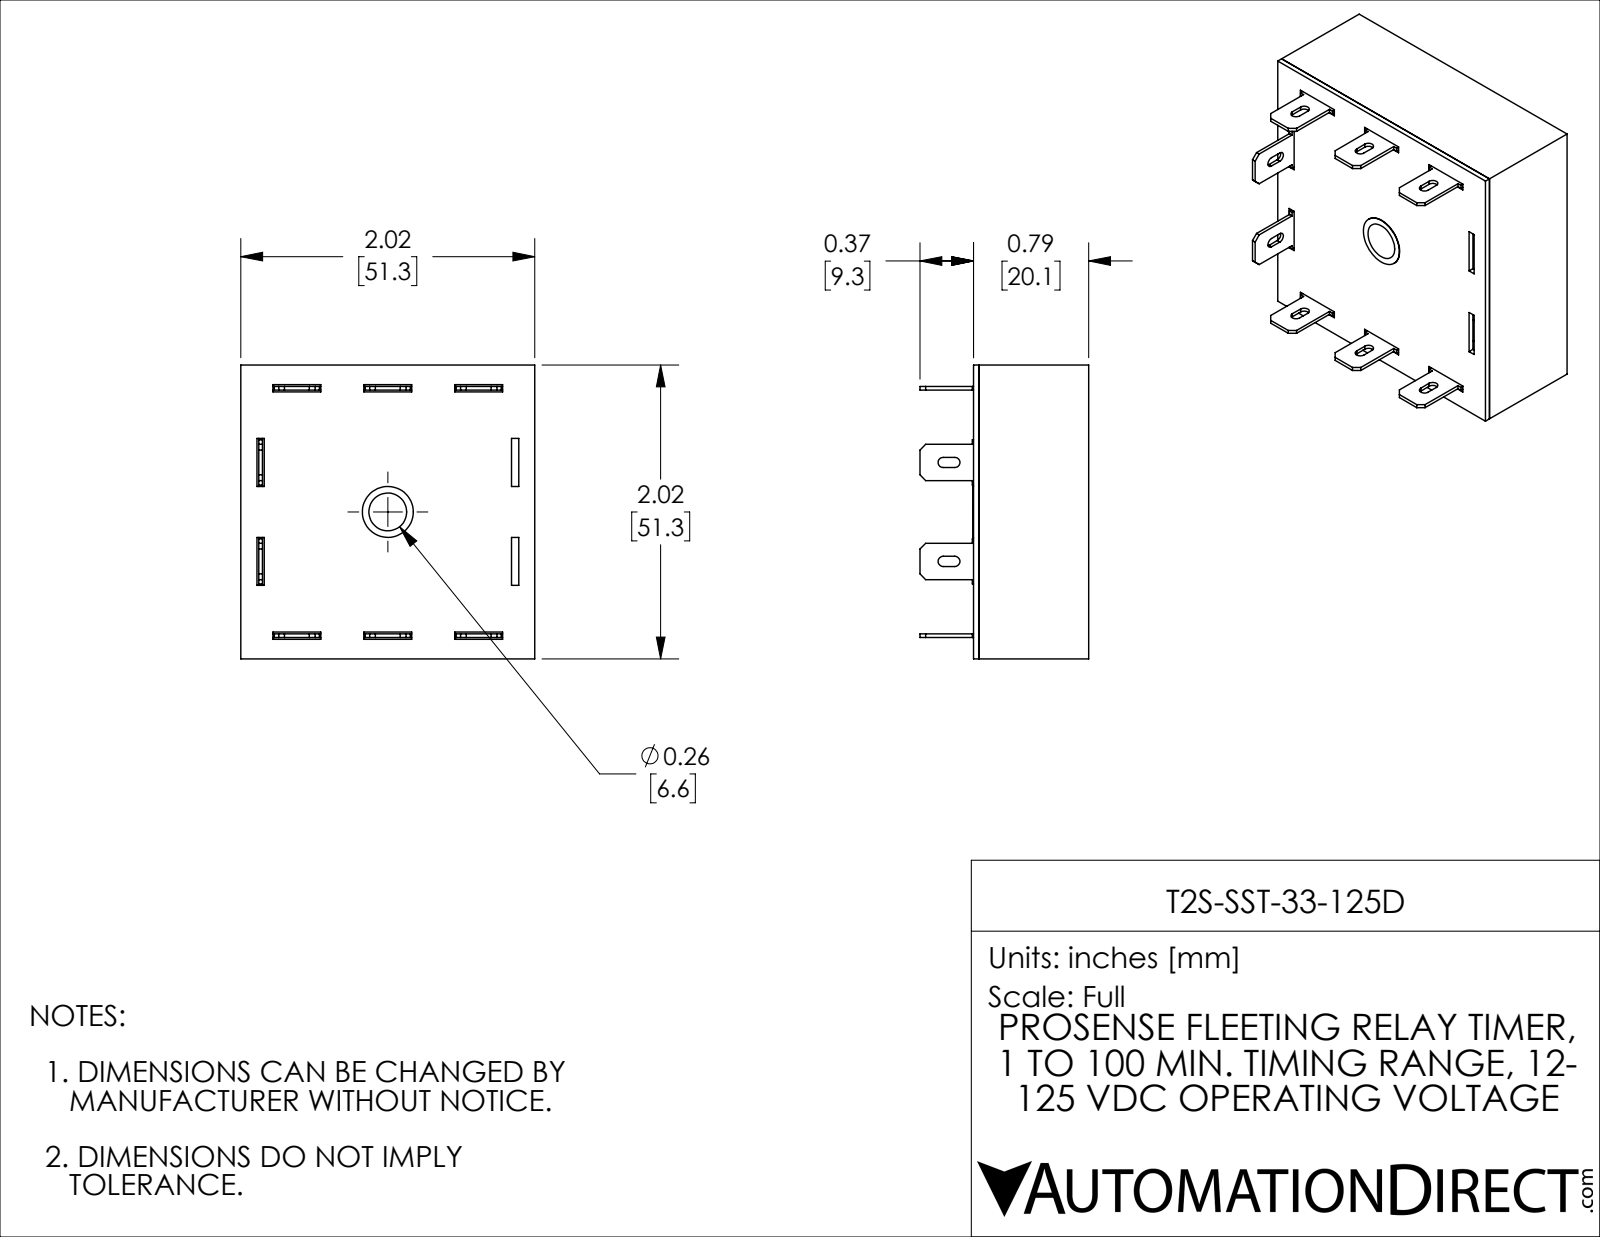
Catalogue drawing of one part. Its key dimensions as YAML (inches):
part_name: "T2S-SST-33-125D"
step_written_by: "SolidWorks 2021 (CONFIG_CONTROL_DESIGN)"
units: inches
bodies: {solids: 10, faces: 256, planar: 234, cylindrical: 20, other: 2}
overall_size: [2.02, 2.02, 1.16]
volume: 0.674
surface_area: 35.37
round_holes:
  - {diameter: 0.35, count: 1}
partial_cylinders:
  - {radius: 0.035, count: 10}
face_to_face_distances: [0.045, 1.975, 0.754, 0.792, 0.038, 0.709, 0.747, 2.02, 1.93, 0.147]
